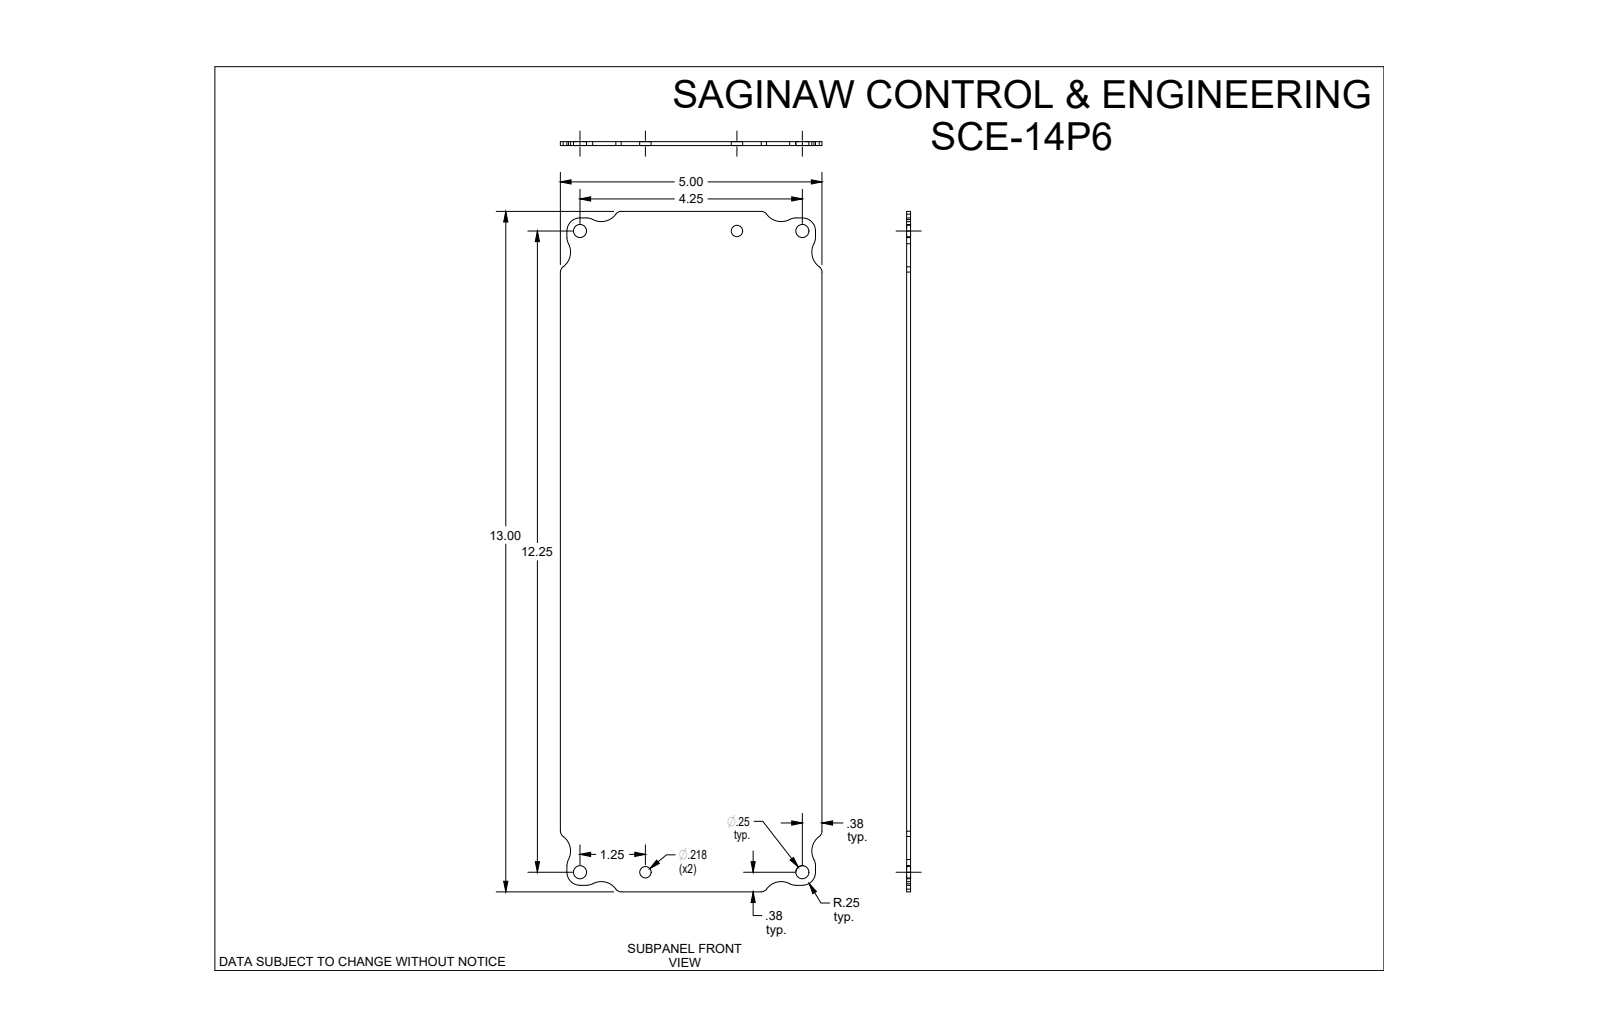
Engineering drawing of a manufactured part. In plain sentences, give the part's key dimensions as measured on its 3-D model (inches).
The part is named "SCE-14P6". Its 3-D file was written by "SolidWorks 2019 (CONFIG_CONTROL_DESIGN)". It is 1 solid with 48 faces: 14 planar, 34 cylindrical and 0 other. Overall it measures 13 by 5 by 0.075 inches. Its volume is 4.764 cubic inches and its surface area 130 square inches. Round holes: 4 of diameter 0.25, 2 of diameter 0.218. Partial cylindrical surfaces (rounded edges, fillets, slot ends): 12 of radius 0.25, 8 of radius 0.125, 8 of radius 0.344. The main face-to-face distances are 0.075, 5, 13, 0.124, 4.876, 0.125, 12.875, 4.752, 12.75. The hole center spacings are 1.25, 3, 4.25, 12.25, 12.313, 12.611, 12.966, 12.374.
